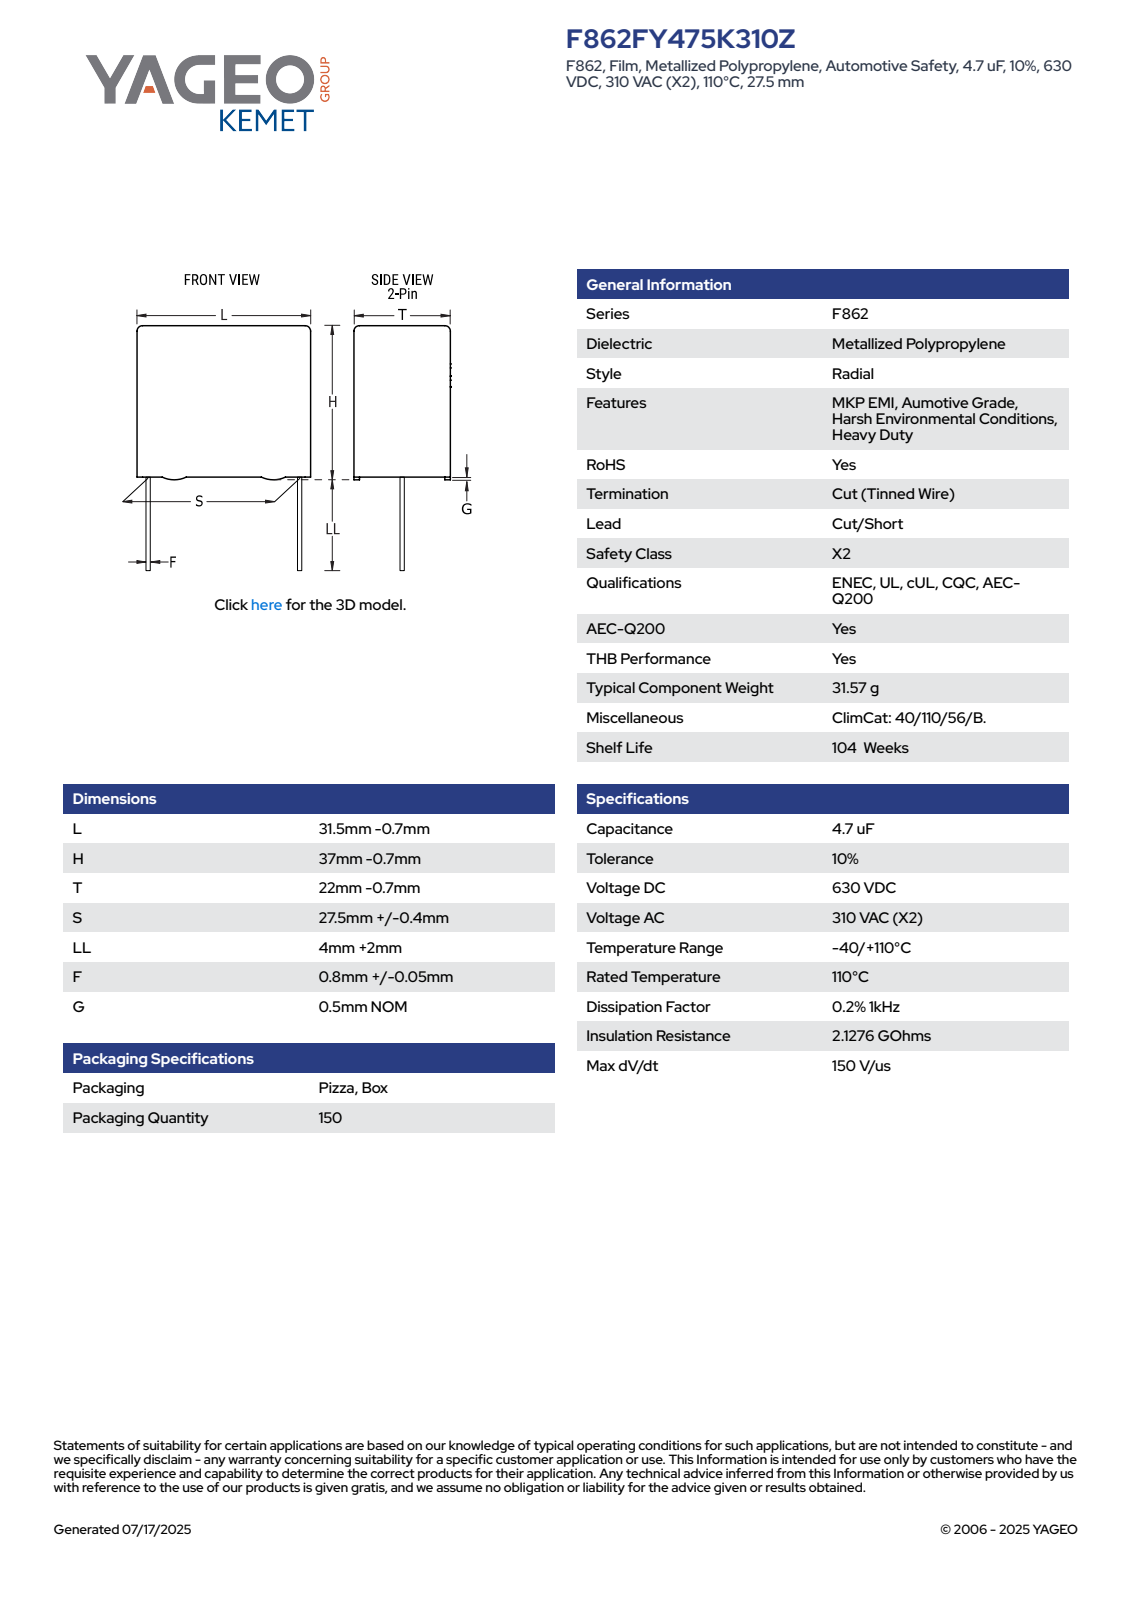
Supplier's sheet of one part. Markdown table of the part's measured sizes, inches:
| quantity | value |
| --- | --- |
| part name | CFR_RBG_31.5X37X22_L30.8H36.3T21.3S27.5LL6F0.85G0.5 |
| STEP written by | SolidWorks 2014 (AUTOMOTIVE_DESIGN) |
| units | inches |
| bodies | 4 solids, 89 faces (81 planar, 8 cylindrical, 0 other) |
| overall size | 1.665 × 1.213 × 0.839 |
| volume | 1.434 in³ |
| surface area | 8.029 in² |
| round bosses / shafts (diameter × count) | 0.033 × 2 |
| partial cylindrical surfaces (radius × count) | 0.02 × 4 |
| main face-to-face distances | 0.839, 1.213, 1.409, 0.02, 1.429, 0.048, 0.791, 0.743, 0.662, 0.663 |
